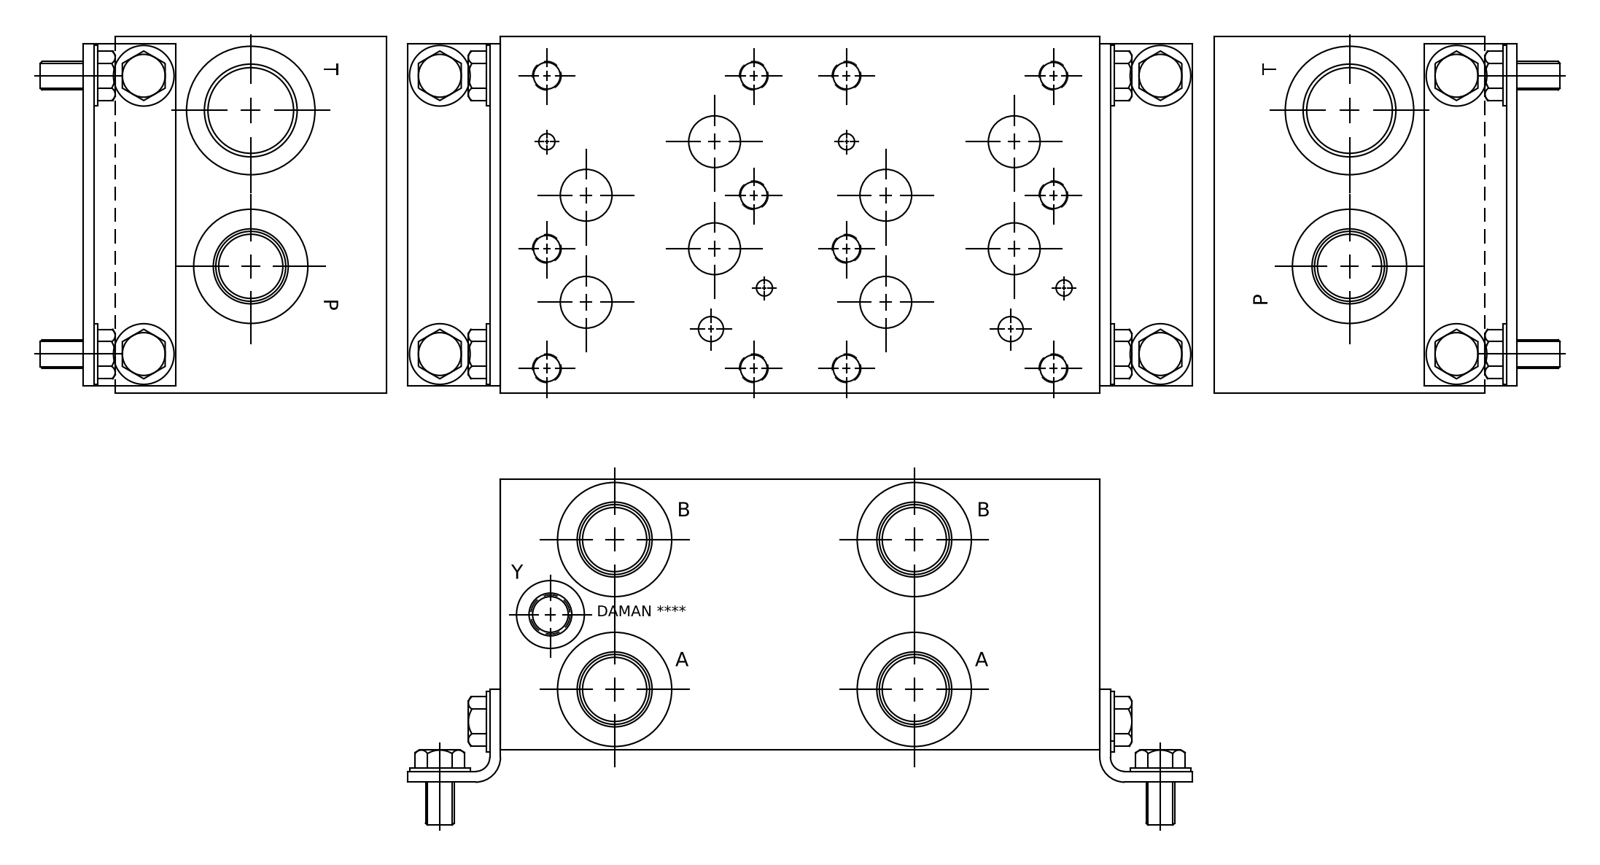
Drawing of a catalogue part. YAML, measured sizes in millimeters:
part_name: "C:\\\\Program Files\\\\PARO\\\\Hydroman 800\\\\Export\\\\AD08P025S_PA_3D"
step_written_by: "Autodesk Inventor 2011 (AUTOMOTIVE_DESIGN)"
units: millimeters
bodies: {solids: 1, faces: 138, planar: 24, cylindrical: 66, other: 48}
overall_size: [266.7, 158.75, 120.65]
volume: 4766000
surface_area: 240518
round_holes:
  - {diameter: 10.72, count: 14}
  - {diameter: 23.01, count: 6}
  - {diameter: 31.27, count: 5}
  - {diameter: 35.51, count: 5}
  - {diameter: 48.97, count: 5}
  - {diameter: 7.14, count: 4}
  - {diameter: 23.02, count: 2}
  - {diameter: 28.57, count: 2}
  - {diameter: 28.58, count: 2}
  - {diameter: 11.11, count: 1}
  - {diameter: 11.13, count: 1}
  - {diameter: 14.3, count: 1}
face_to_face_distances: [120.65, 158.75, 266.7, 0.79, 265.91, 157.96, 265.12, 4.06, 3.27, 262.64]
hole_center_spacings: [133.35, 29.54, 76.99, 152.67, 159.45, 61.92, 74.6, 118.29]
